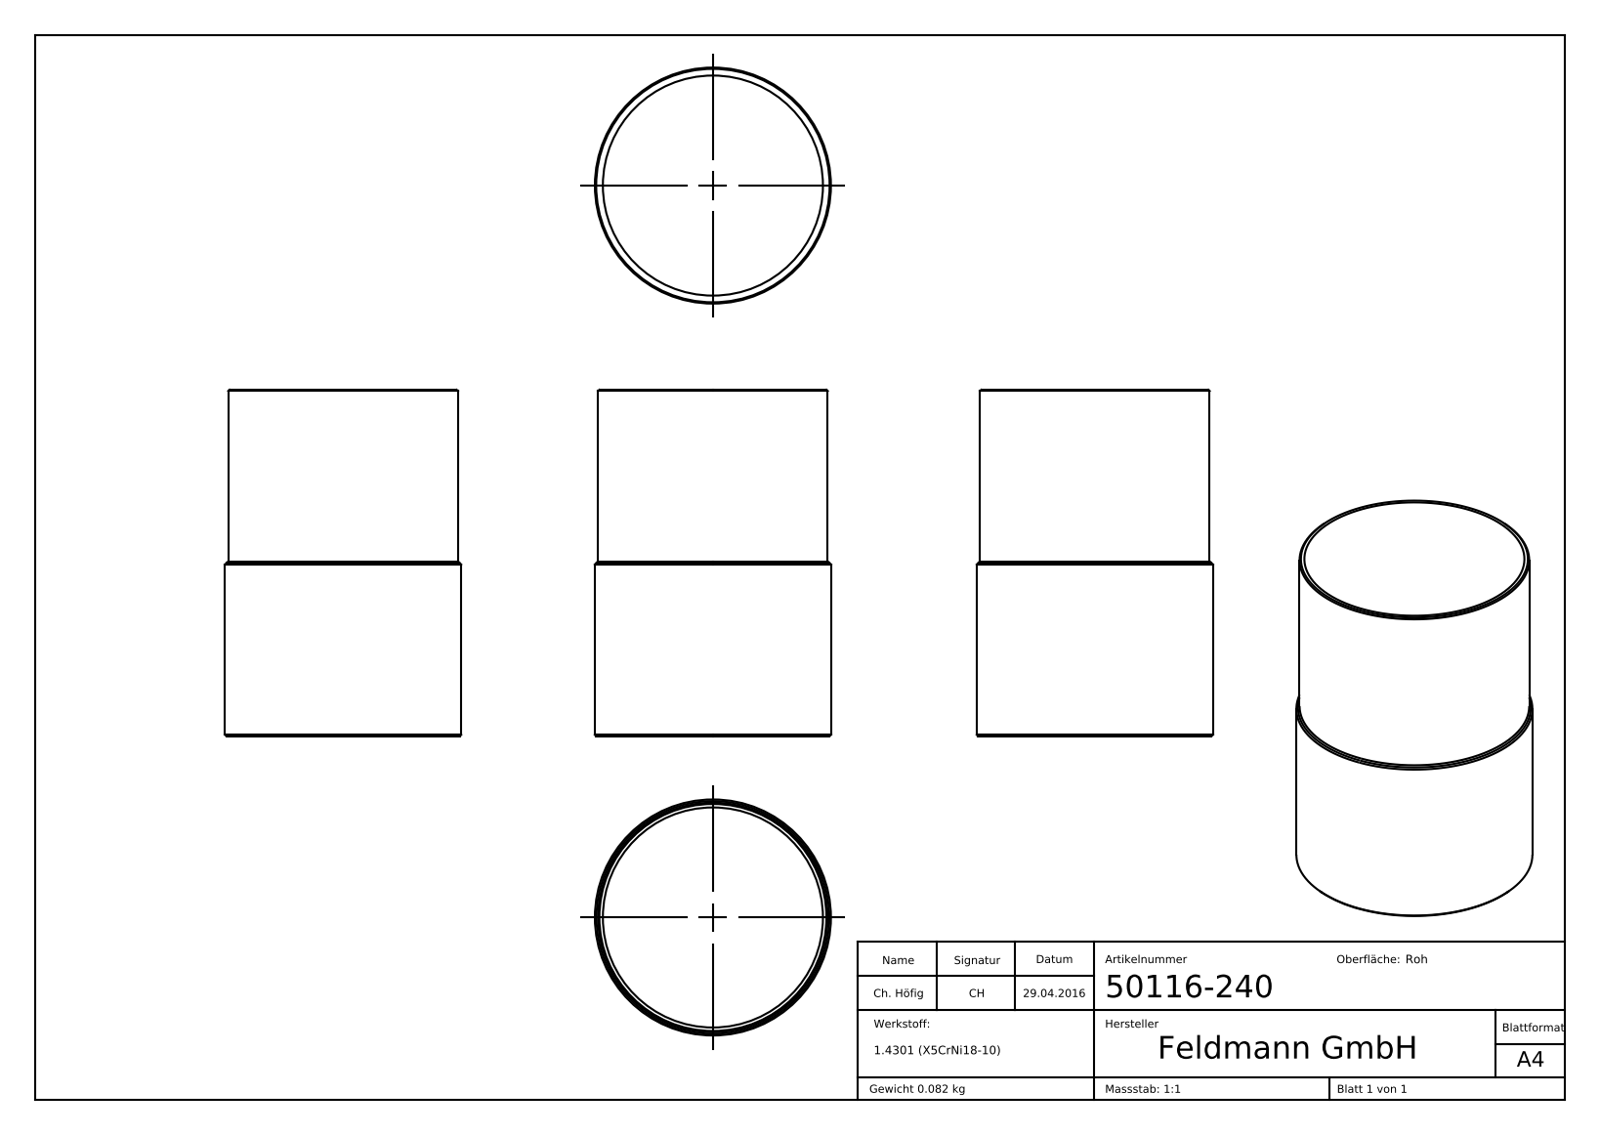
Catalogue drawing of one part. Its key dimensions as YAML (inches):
part_name: "50116-240"
step_written_by: "SolidWorks 2015 (CONFIG_CONTROL_DESIGN)"
units: inches
bodies: {solids: 1, faces: 227, planar: 100, cylindrical: 30, other: 97}
overall_size: [2.559, 1.744, 1.744]
volume: 0.636
surface_area: 27.41
round_holes:
  - {diameter: 1.626, count: 1}
round_bosses_or_shafts:
  - {diameter: 1.744, count: 1}
  - {diameter: 1.697, count: 1}
partial_cylinders:
  - {radius: 0.817, count: 1}
face_to_face_distances: [2.559, 0.04, 0.462, 0.502, 0.052, 0.576, 0.333, 0.373, 0.015, 0.246]
